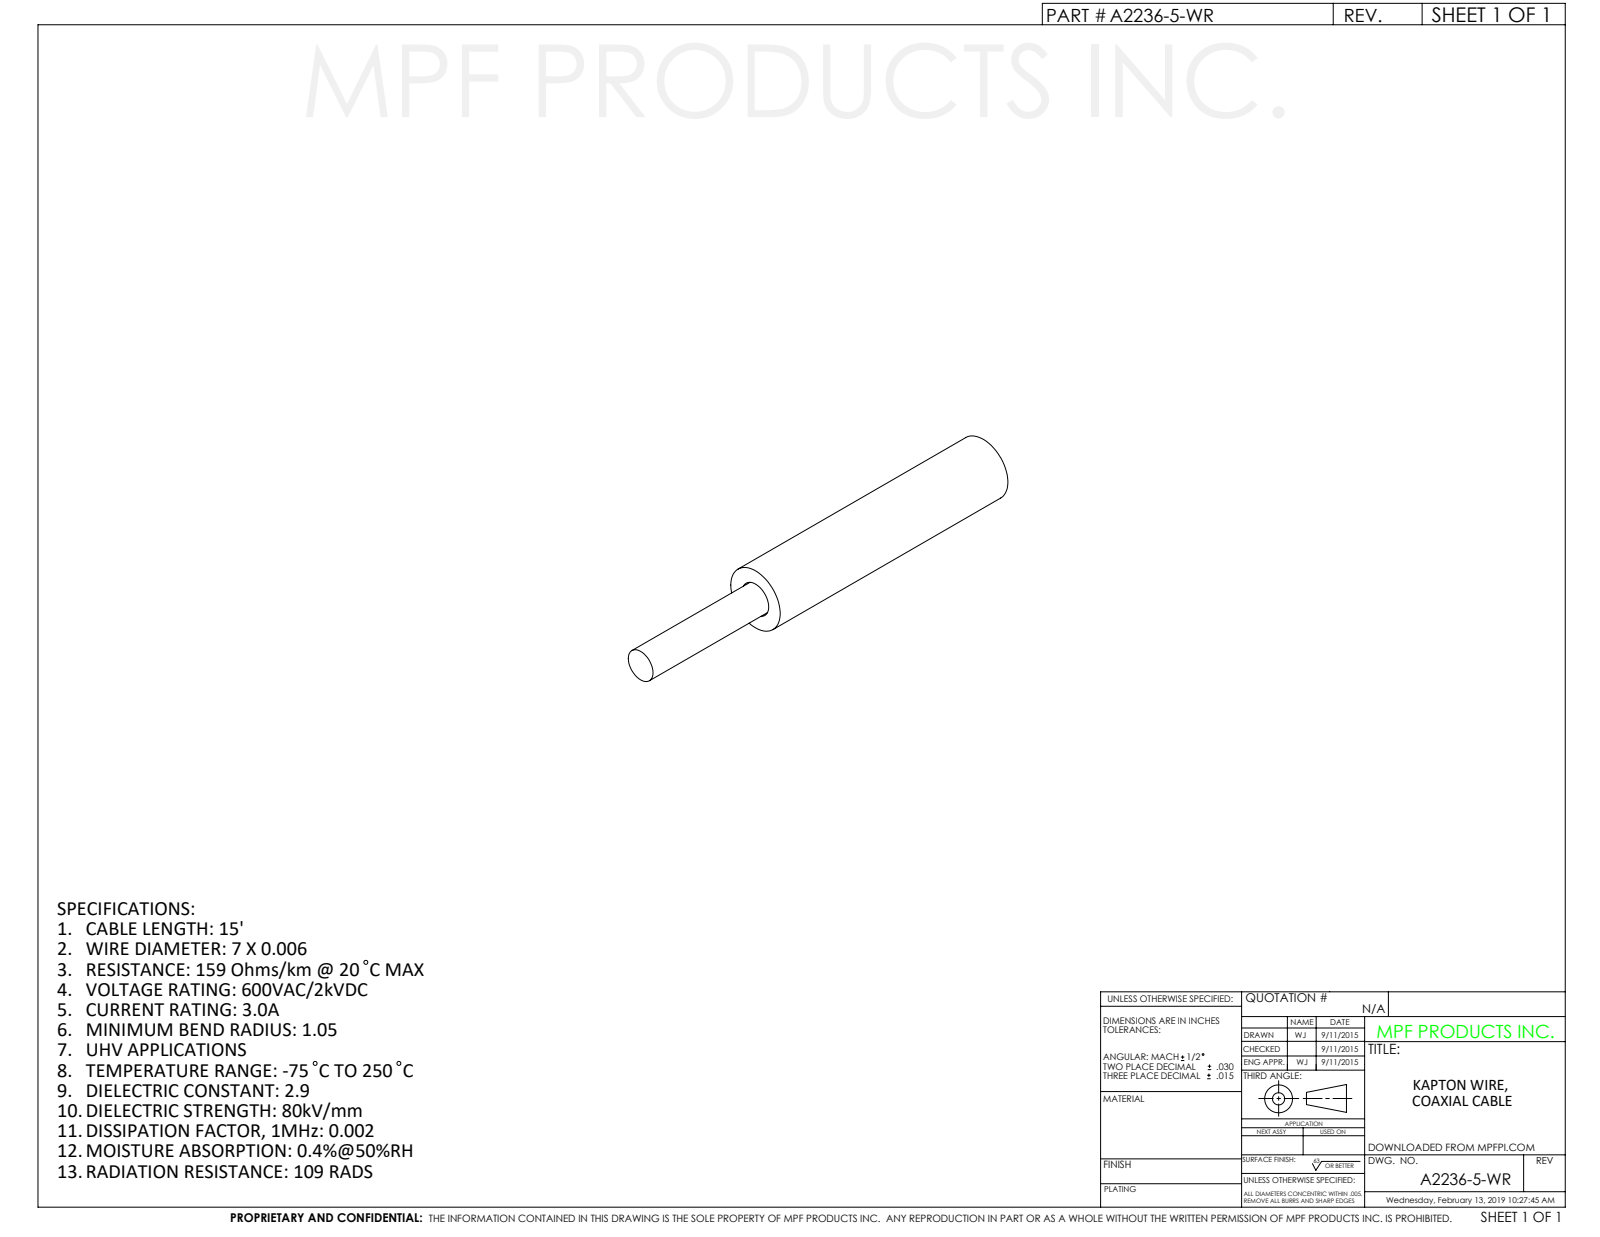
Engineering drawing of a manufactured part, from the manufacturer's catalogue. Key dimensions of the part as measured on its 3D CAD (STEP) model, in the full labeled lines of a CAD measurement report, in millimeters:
Part name (STEP PRODUCT): A2236-5-WR
STEP written by: SolidWorks 2012 (CONFIG_CONTROL_DESIGN)
Units: millimetres
Bodies: 10 solids, 390 faces (20 planar, 98 cylindrical, 272 other)
Overall size (bounding box): 8.9 × 2.3 × 2.3
Volume: 20 mm³ · Surface area: 236 mm²
Round holes (diameter × count): ⌀0.6 ×1, ⌀1.7 ×1, ⌀2.1 ×1
Round bosses / shafts (diameter × count): ⌀0.2 ×7, ⌀2.3 ×1, ⌀2 ×1, ⌀1.6 ×1
Partial cylindrical surfaces — rounded edges, fillets, slot ends (radius × count): R1 ×1
Main face-to-face distances: 7.6, 5.7, 1.9, 5.1, 0.6, 2.5, 8.9, 3.8, 3.2, 1.3
